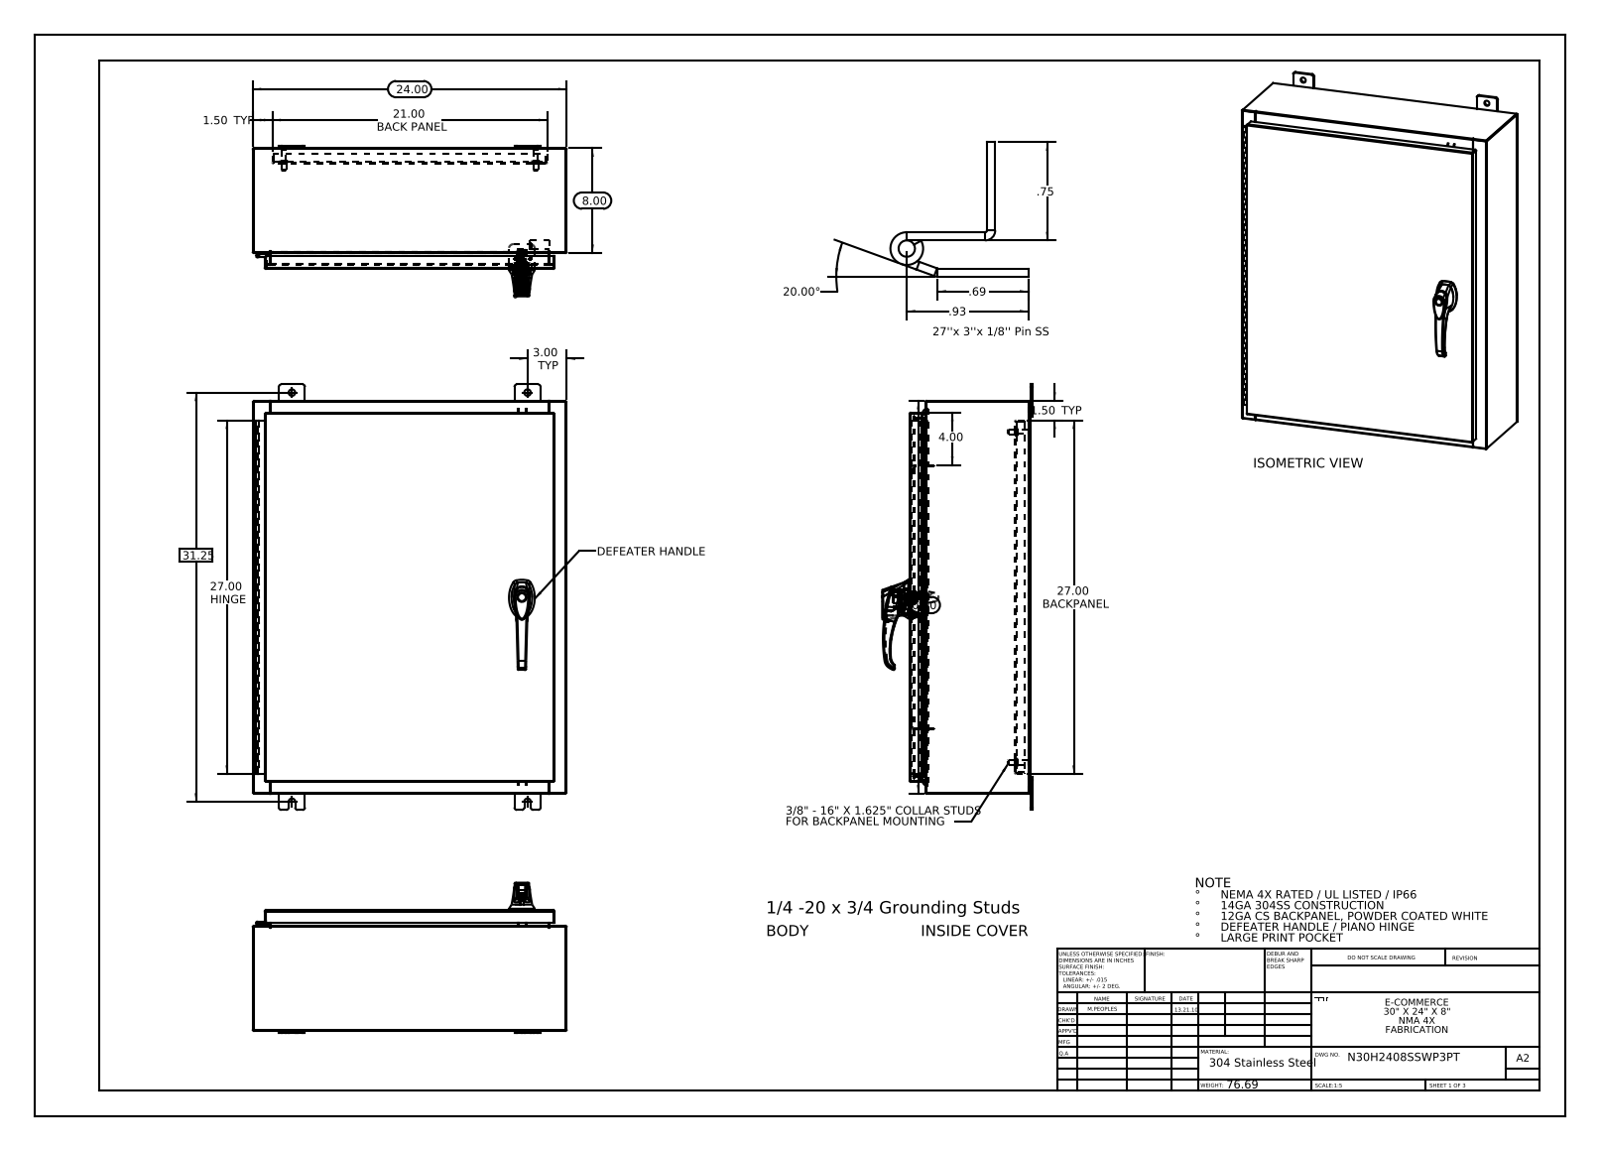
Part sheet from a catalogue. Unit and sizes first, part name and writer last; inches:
Units: inches
Overall size (bounding box): 32.5 × 24 × 11.495
Round holes (diameter × count): ⌀0.5 ×8, ⌀0.25 ×4, ⌀0.138 ×3, ⌀0.161 ×3, ⌀0.079 ×2, ⌀0.203 ×2, ⌀0.313 ×2, ⌀0.437 ×2, ⌀0.125 ×1, ⌀0.125 ×1, ⌀0.197 ×1, ⌀0.276 ×1
Round bosses / shafts (diameter × count): ⌀0.625 ×4, ⌀0.375 ×4, ⌀0.33 ×4, ⌀1.181 ×1, ⌀0.748 ×1, ⌀0.68 ×1, ⌀0.661 ×1, ⌀0.639 ×1
Partial cylindrical surfaces — rounded edges, fillets, slot ends (radius × count): R0.118 ×37, R0.006 ×33, R0.013 ×24, R0.19 ×24, R0.088 ×18, R0.039 ×15, R0.028 ×12, R0.008 ×6
Main face-to-face distances: 0.075, 9.126, 0.104, 9.051, 9.201, 1, 1.075, 8.051, 8.126, 1.179
Hole centre spacings: 8.369, 0.295, 0.625, 0.841, 1.25, 1.313, 1.561, 1.858
Volume: 272.1 in³ · Surface area: 6 712 in²
Bodies: 31 solids, 2576 faces (953 planar, 969 cylindrical, 654 other)
Part name (STEP PRODUCT): 00005309_G26103101; N30H2408SSWP3PT Bottom; N30H2408SSWP3PT Defeater Handle Rod; g26103103_26163303 (+8 more)
STEP written by: SolidWorks 2013 (CONFIG_CONTROL_DESIGN)
